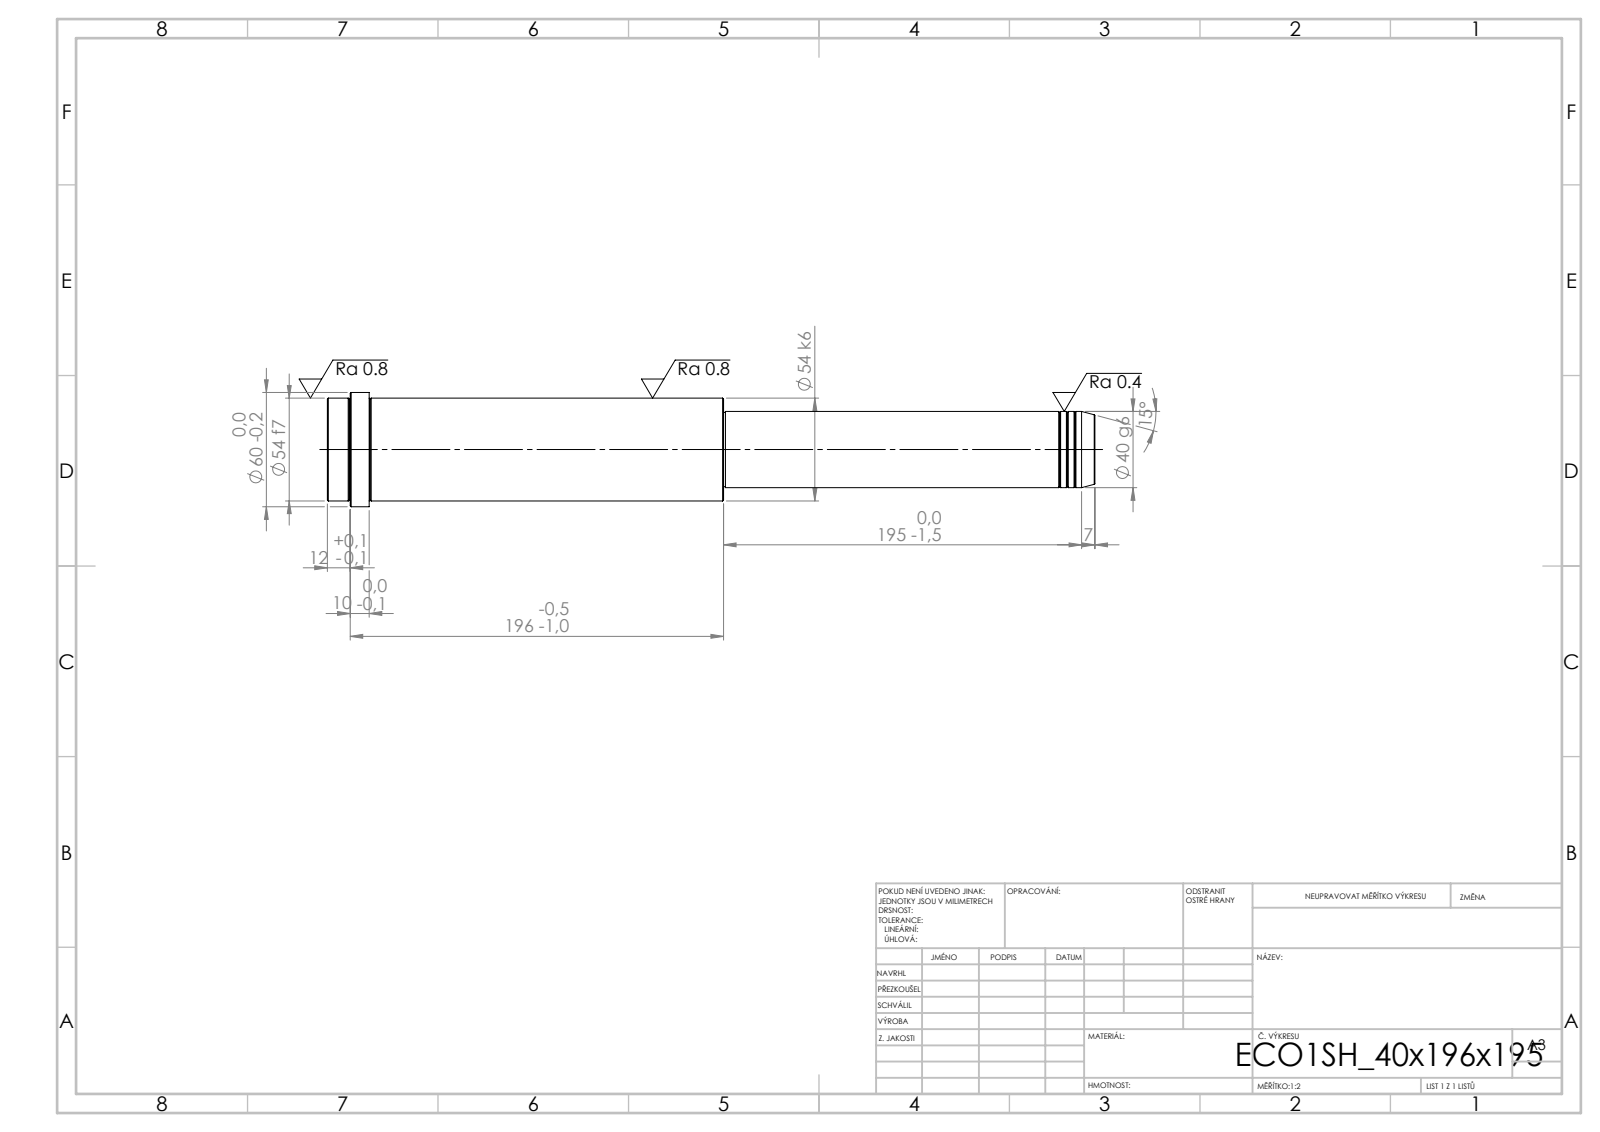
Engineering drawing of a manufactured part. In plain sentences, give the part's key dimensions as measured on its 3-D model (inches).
Its 3-D file was written by "SolidWorks 2019 (CONFIG_CONTROL_DESIGN)". It is 1 solid with 52 faces: 6 planar, 16 cylindrical and 30 other. Overall it measures 15.866 by 2.362 by 2.362 inches. Its volume is 44.28 cubic inches and its surface area 101.9 square inches. Round bosses or shafts: 1 of diameter 2.362, 1 of diameter 2.126, 1 of diameter 1.575, 1 of diameter 1.535. The main face-to-face distances are 8.189, 7.677, 15.866, 15, 7.323, 0.866, 15.394, 7.717, 0.394, 0.472.
